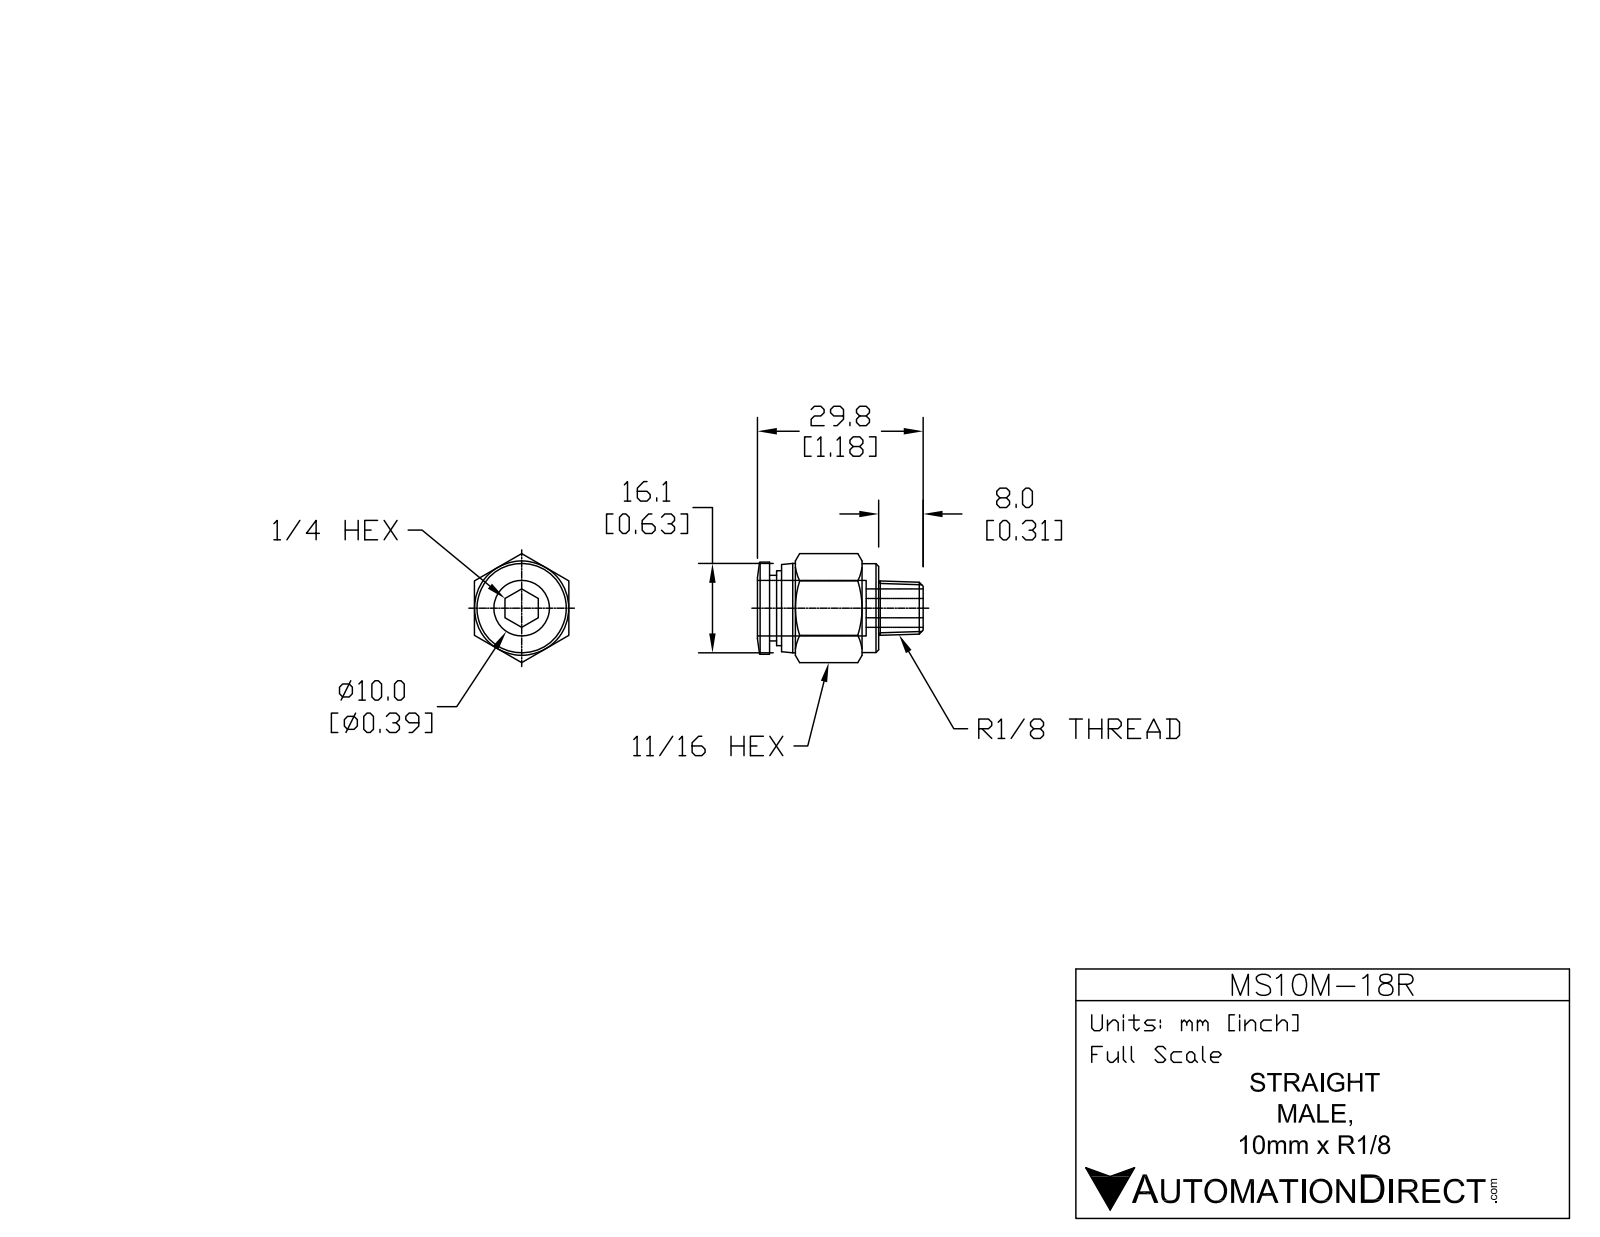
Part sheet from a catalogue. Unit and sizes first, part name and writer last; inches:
Units: inches
Overall size (bounding box): 1.175 × 0.773 × 0.669
Round holes (diameter × count): ⌀0.236 ×1, ⌀0.406 ×1
Round bosses / shafts (diameter × count): ⌀0.654 ×1, ⌀0.634 ×1, ⌀0.63 ×1, ⌀0.531 ×1, ⌀0.465 ×1
Main face-to-face distances: 0.669, 0.774, 0.089, 0.685, 0.689, 0.6, 0.085, 0.724, 0.636, 0.035
Volume: 0.21 in³ · Surface area: 4.363 in²
Bodies: 1 solid, 55 faces (15 planar, 14 cylindrical, 26 other)
Part name (STEP PRODUCT): MS10M-18R
STEP written by: SolidWorks 2015 (AUTOMOTIVE_DESIGN)
